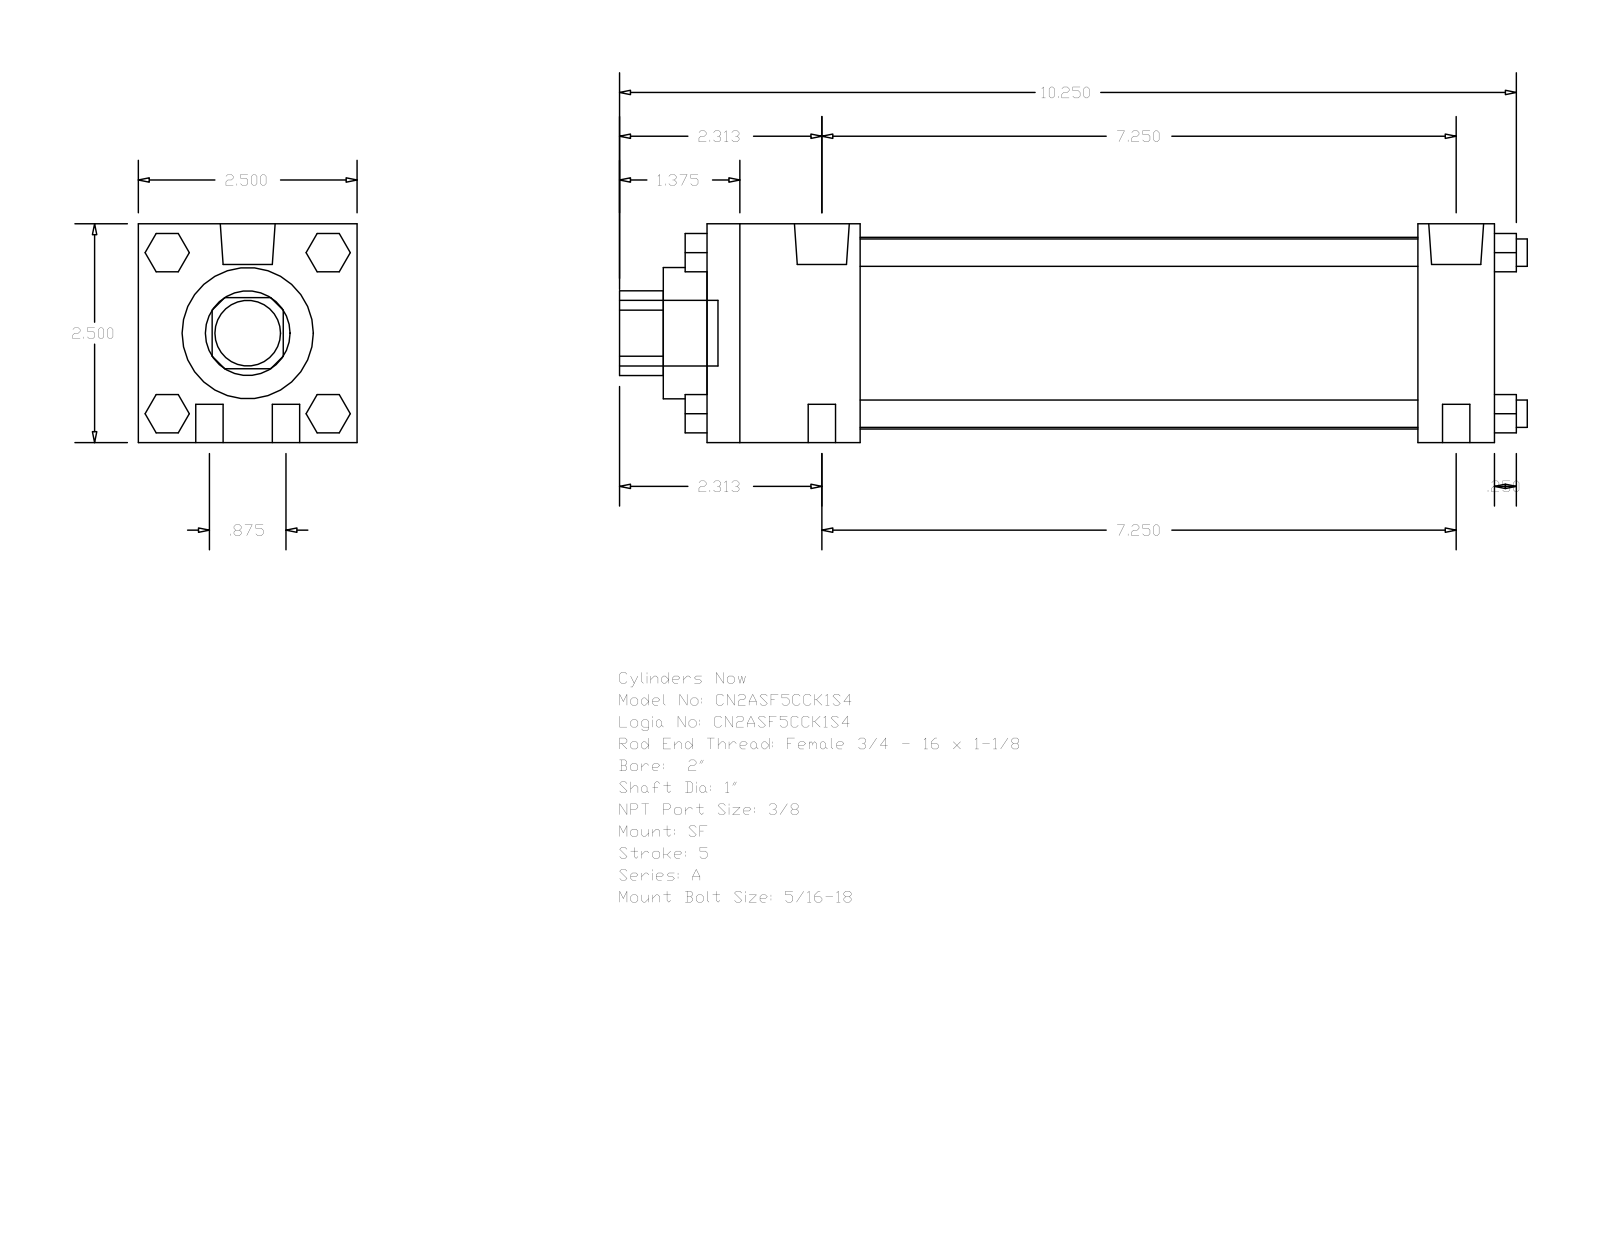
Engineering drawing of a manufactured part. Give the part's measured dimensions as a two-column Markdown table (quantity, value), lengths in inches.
| quantity | value |
| --- | --- |
| part name | A_SF__0200_1 |
| STEP written by | GSSL Pune (CONFIG_CONTROL_DESIGN) |
| units | inches |
| bodies | 0 solids, 124 faces (94 planar, 30 cylindrical, 0 other) |
| overall size | 10.375 × 2.5 × 2.5 |
| round holes (diameter × count) | 1 × 1, 1.5 × 1, 2.19 × 1 |
| round bosses / shafts (diameter × count) | 0.313 × 8, 0.627 × 2, 0.219 × 2, 0.75 × 1 |
| partial cylindrical surfaces (radius × count) | 0.484 × 1 |
| main face-to-face distances | 2.5, 9, 8.125, 0.875, 1.75, 6.375, 7.25, 0.5, 9.5, 0.25 |
